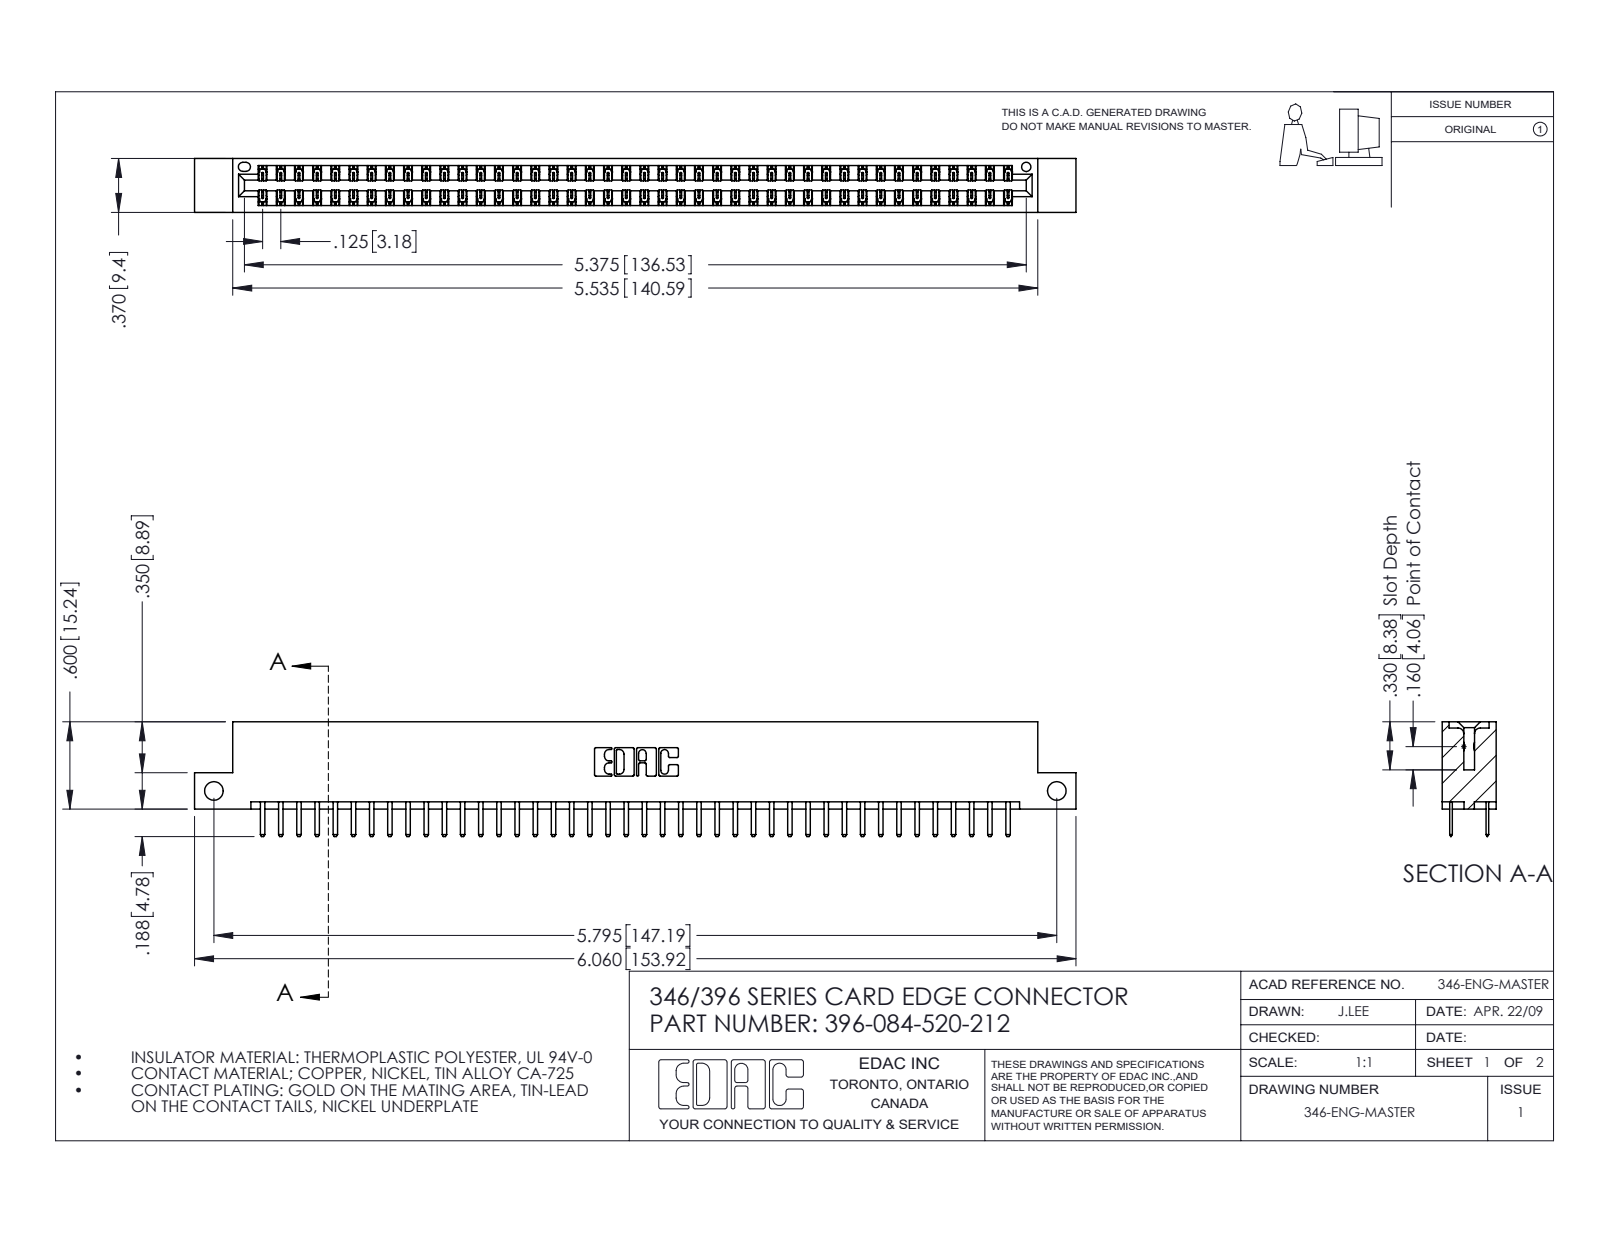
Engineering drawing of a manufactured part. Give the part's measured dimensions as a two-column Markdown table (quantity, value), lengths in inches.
| quantity | value |
| --- | --- |
| part name | 396-084-520-212; 346 Part_Flush Mounting Lugs - Side Mount; 345-292-001_345-293-120 |
| STEP written by | SolidWorks 2016 (CONFIG_CONTROL_DESIGN) |
| units | inches |
| bodies | 85 solids, 4826 faces (3184 planar, 1642 cylindrical, 0 other) |
| overall size | 6.06 × 0.788 × 0.37 |
| volume | 0.908 in³ |
| surface area | 31.37 in² |
| round holes (diameter × count) | 0.128 × 2, 0.064 × 1 |
| partial cylindrical surfaces (radius × count) | 0.006 × 126, 0.01 × 88, 0.01 × 22, 0.007 × 6, 0.031 × 6, 0.026 × 3, 0.014 × 2, 0.022 × 2 |
| main face-to-face distances | 0.048, 0.322, 0.25, 0.37, 0.275, 0.072, 0.298, 0.025, 0.148, 0.222 |
| hole center spacings | 5.795 |
